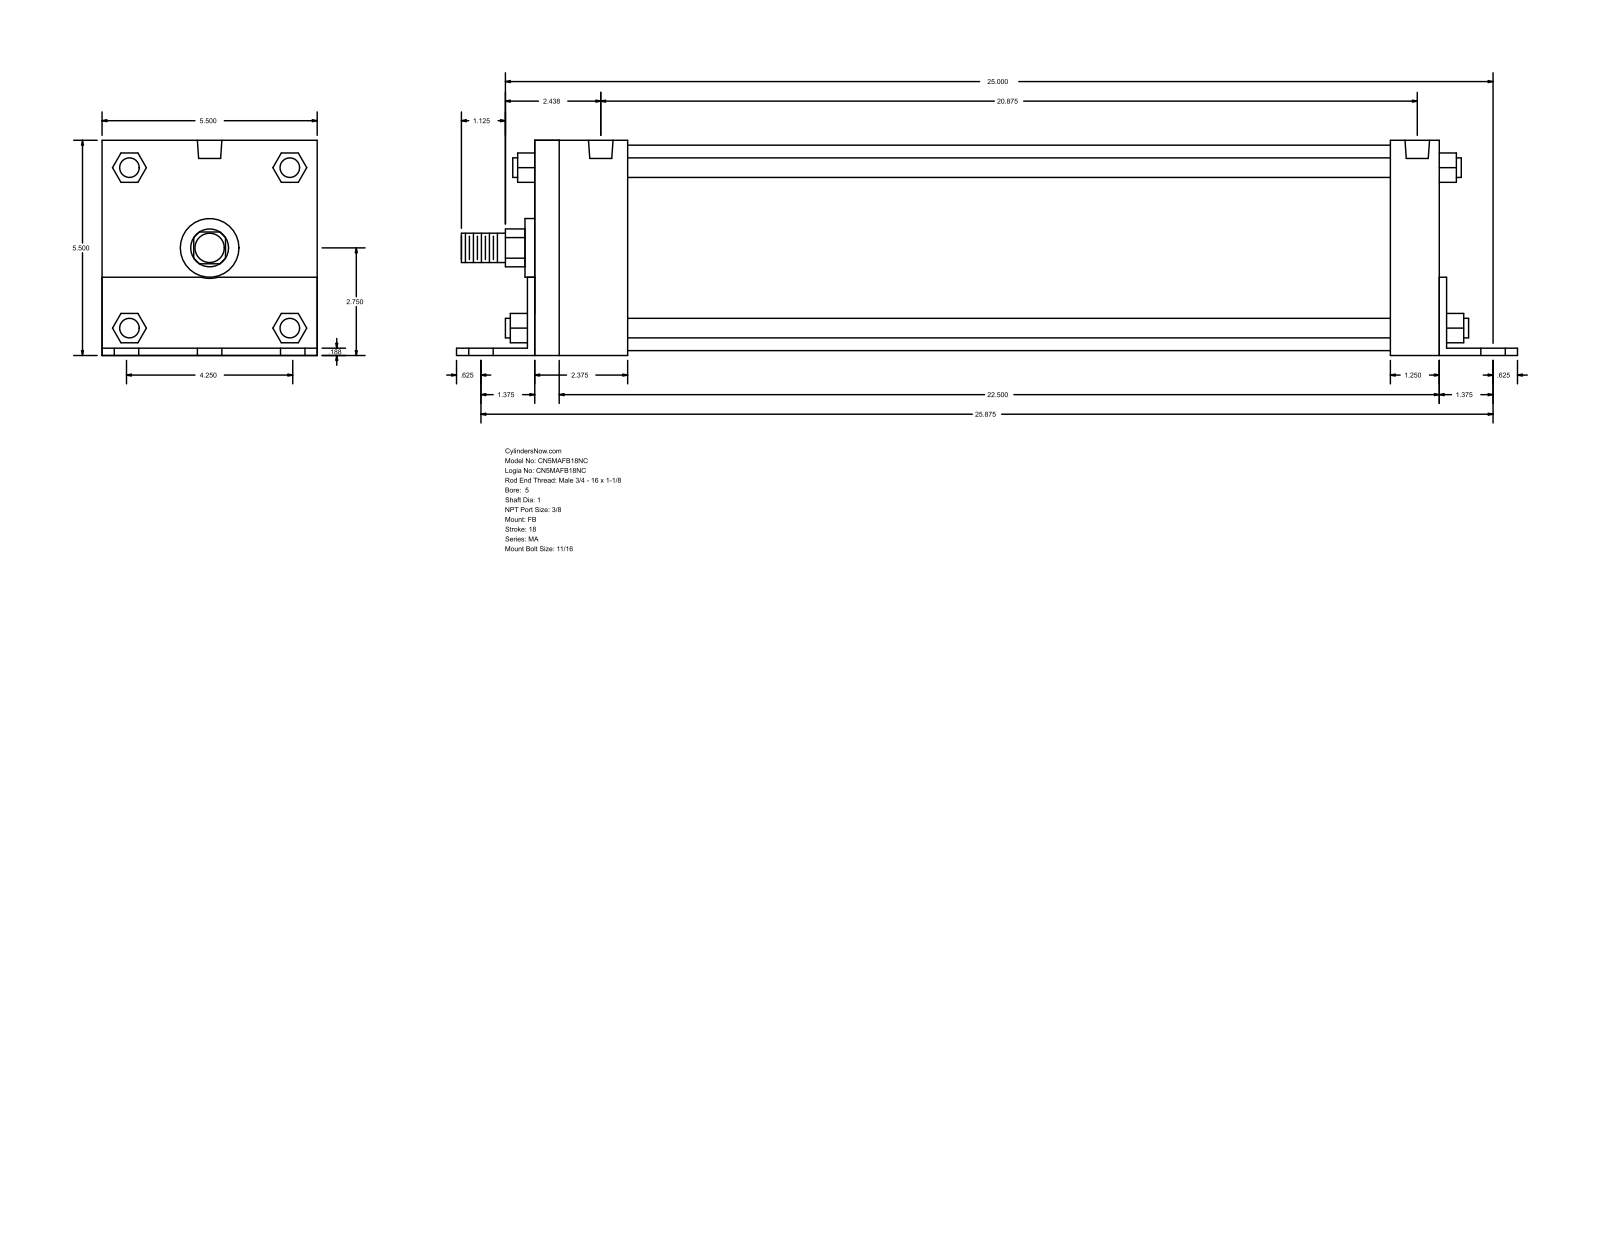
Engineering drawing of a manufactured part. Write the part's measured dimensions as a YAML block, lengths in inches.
part_name: "MA_FB__0500_1"
step_written_by: "GSSL Pune (CONFIG_CONTROL_DESIGN)"
units: inches
bodies: {solids: 0, faces: 140, planar: 105, cylindrical: 35, other: 0}
overall_size: [27.125, 5.502, 5.5]
round_holes:
  - {diameter: 0.687, count: 6}
  - {diameter: 0.437, count: 4}
  - {diameter: 0.627, count: 2}
round_bosses_or_shafts:
  - {diameter: 0.5, count: 4}
  - {diameter: 5.25, count: 1}
  - {diameter: 1.5, count: 1}
  - {diameter: 1, count: 1}
  - {diameter: 0.75, count: 1}
partial_cylinders:
  - {radius: 0.484, count: 1}
  - {radius: 0.78, count: 1}
face_to_face_distances: [5.5, 0.187, 5.502, 0.185, 5.315, 23.125, 0.188, 23.313, 23.312, 23.5]
hole_center_spacings: [2.125, 25.962, 25.875, 0.187, 2.876, 3.005, 3.728, 3.883]
